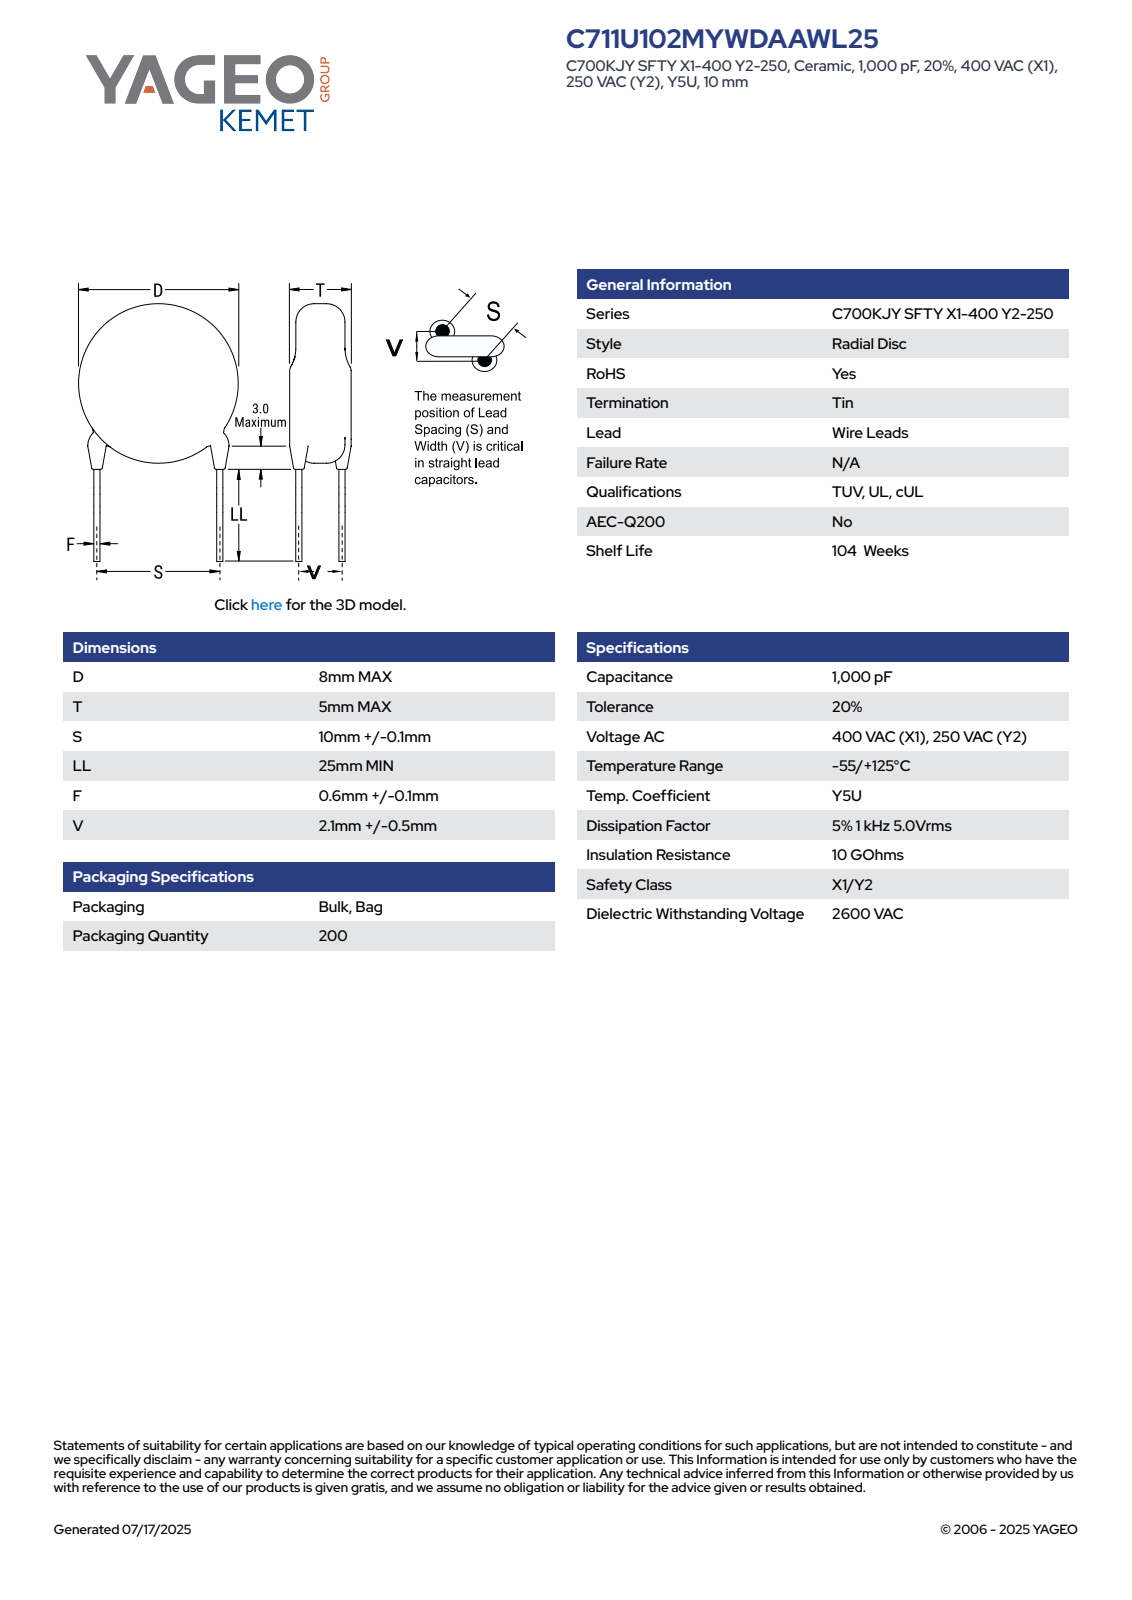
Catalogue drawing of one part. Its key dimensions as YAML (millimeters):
part_name: "CCD_KST_8X5_D8T5S10.1LL25F0.7V2.1"
step_written_by: "SolidWorks 2021 (AUTOMOTIVE_DESIGN)"
units: millimeters
bodies: {solids: 4, faces: 81, planar: 63, cylindrical: 14, other: 4}
overall_size: [34.5, 11.2, 5]
volume: 271
surface_area: 354
round_bosses_or_shafts:
  - {diameter: 1.2, count: 4}
  - {diameter: 0.7, count: 2}
  - {diameter: 8, count: 1}
face_to_face_distances: [5, 25, 0.97, 31.02, 6.02, 30.05, 5.05, 0.36, 0.78, 3.96]
